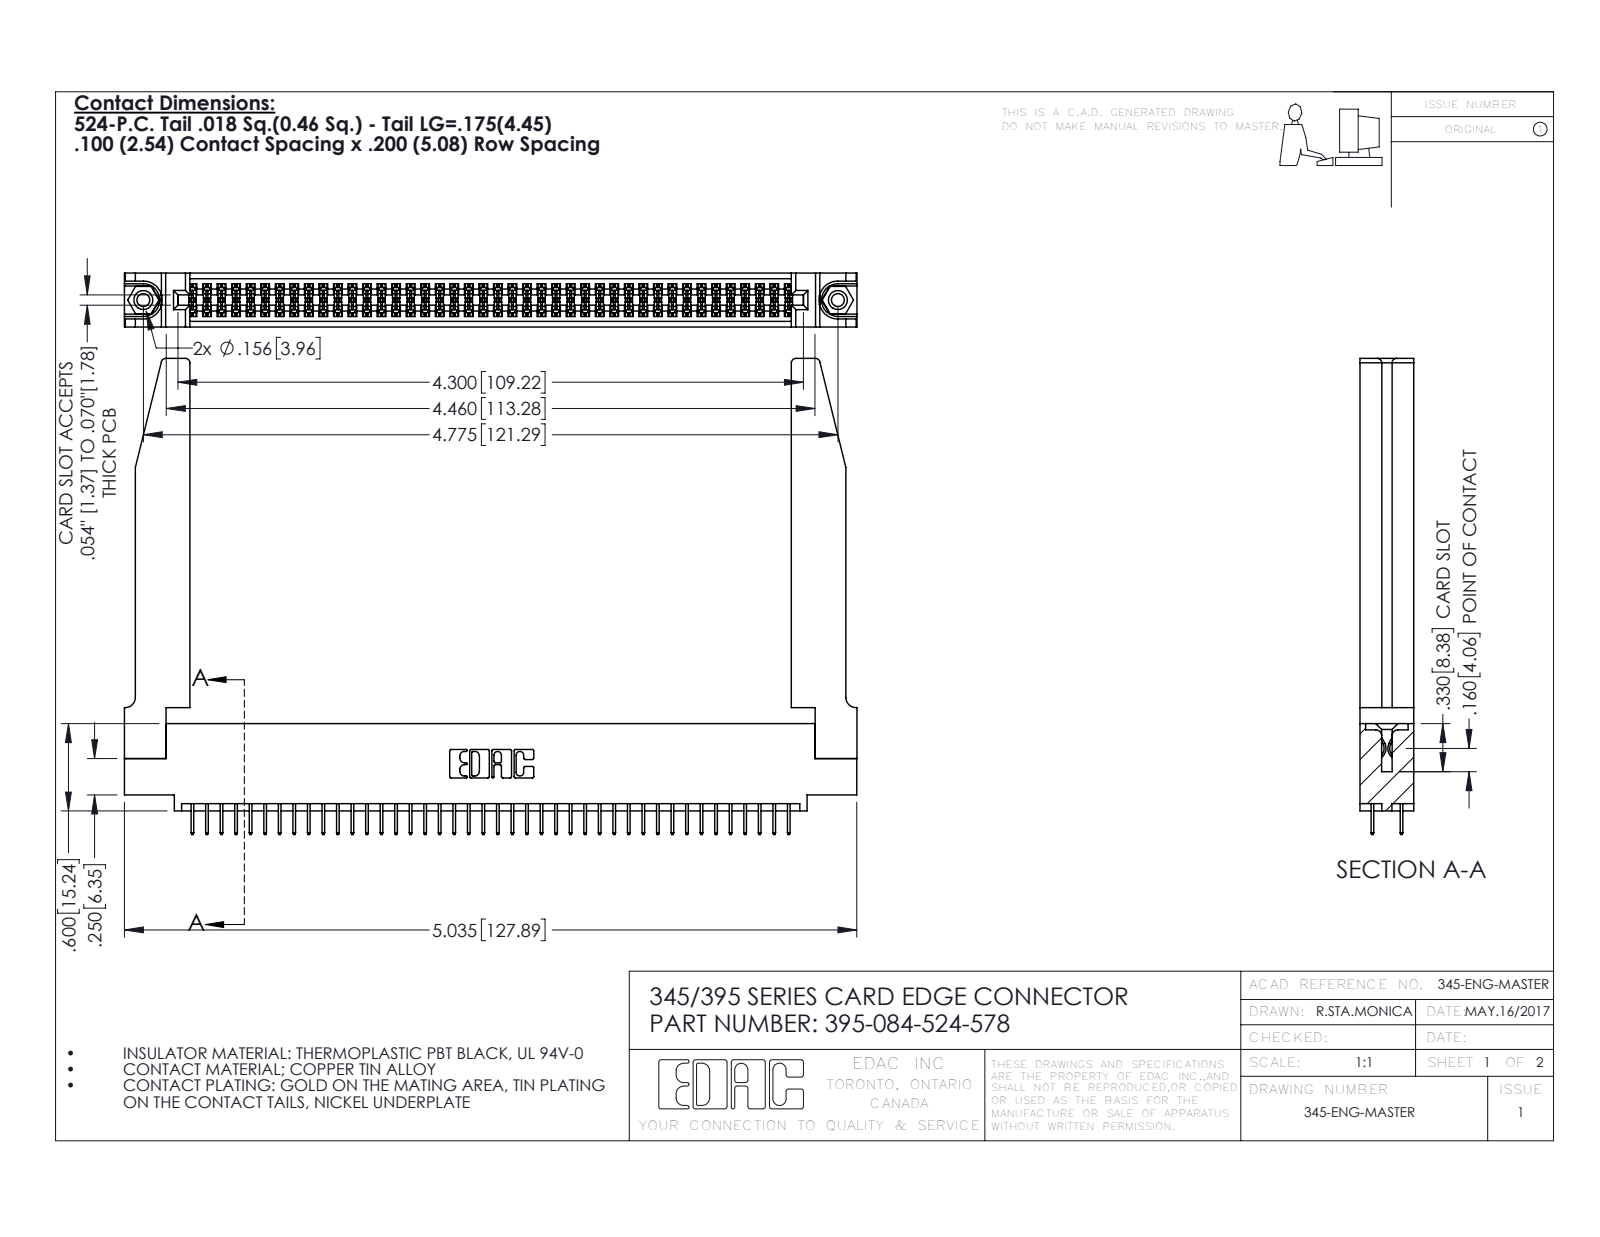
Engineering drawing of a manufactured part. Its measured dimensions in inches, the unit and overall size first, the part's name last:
Units: inches
Overall size (bounding box): 5.036 × 3.272 × 0.37
Round holes (diameter × count): ⌀0.089 ×2, ⌀0.125 ×2, ⌀0.156 ×2, ⌀0.064 ×1
Round bosses / shafts (diameter × count): ⌀0.155 ×2
Partial cylindrical surfaces — rounded edges, fillets, slot ends (radius × count): R0.006 ×126, R0.01 ×22, R0.03 ×8, R0.007 ×6, R0.031 ×6, R0.026 ×3, R0.014 ×2, R0.019 ×2
Main face-to-face distances: 0.37, 0.072, 0.298, 0.2, 0.098, 0.272, 0.025, 0.225, 0.148, 0.15
Hole centre spacings: 0.27, 4.539, 4.775
Volume: 1.22 in³ · Surface area: 38.23 in²
Bodies: 89 solids, 4900 faces (3502 planar, 1346 cylindrical, 52 other)
Part name (STEP PRODUCT): 345-220-078_345-220-078; 345-292-001_345-293-124; 395-084-524-578; 345-250-001_345-250-001-102 (+1 more)
STEP written by: SolidWorks 2016 (CONFIG_CONTROL_DESIGN)
